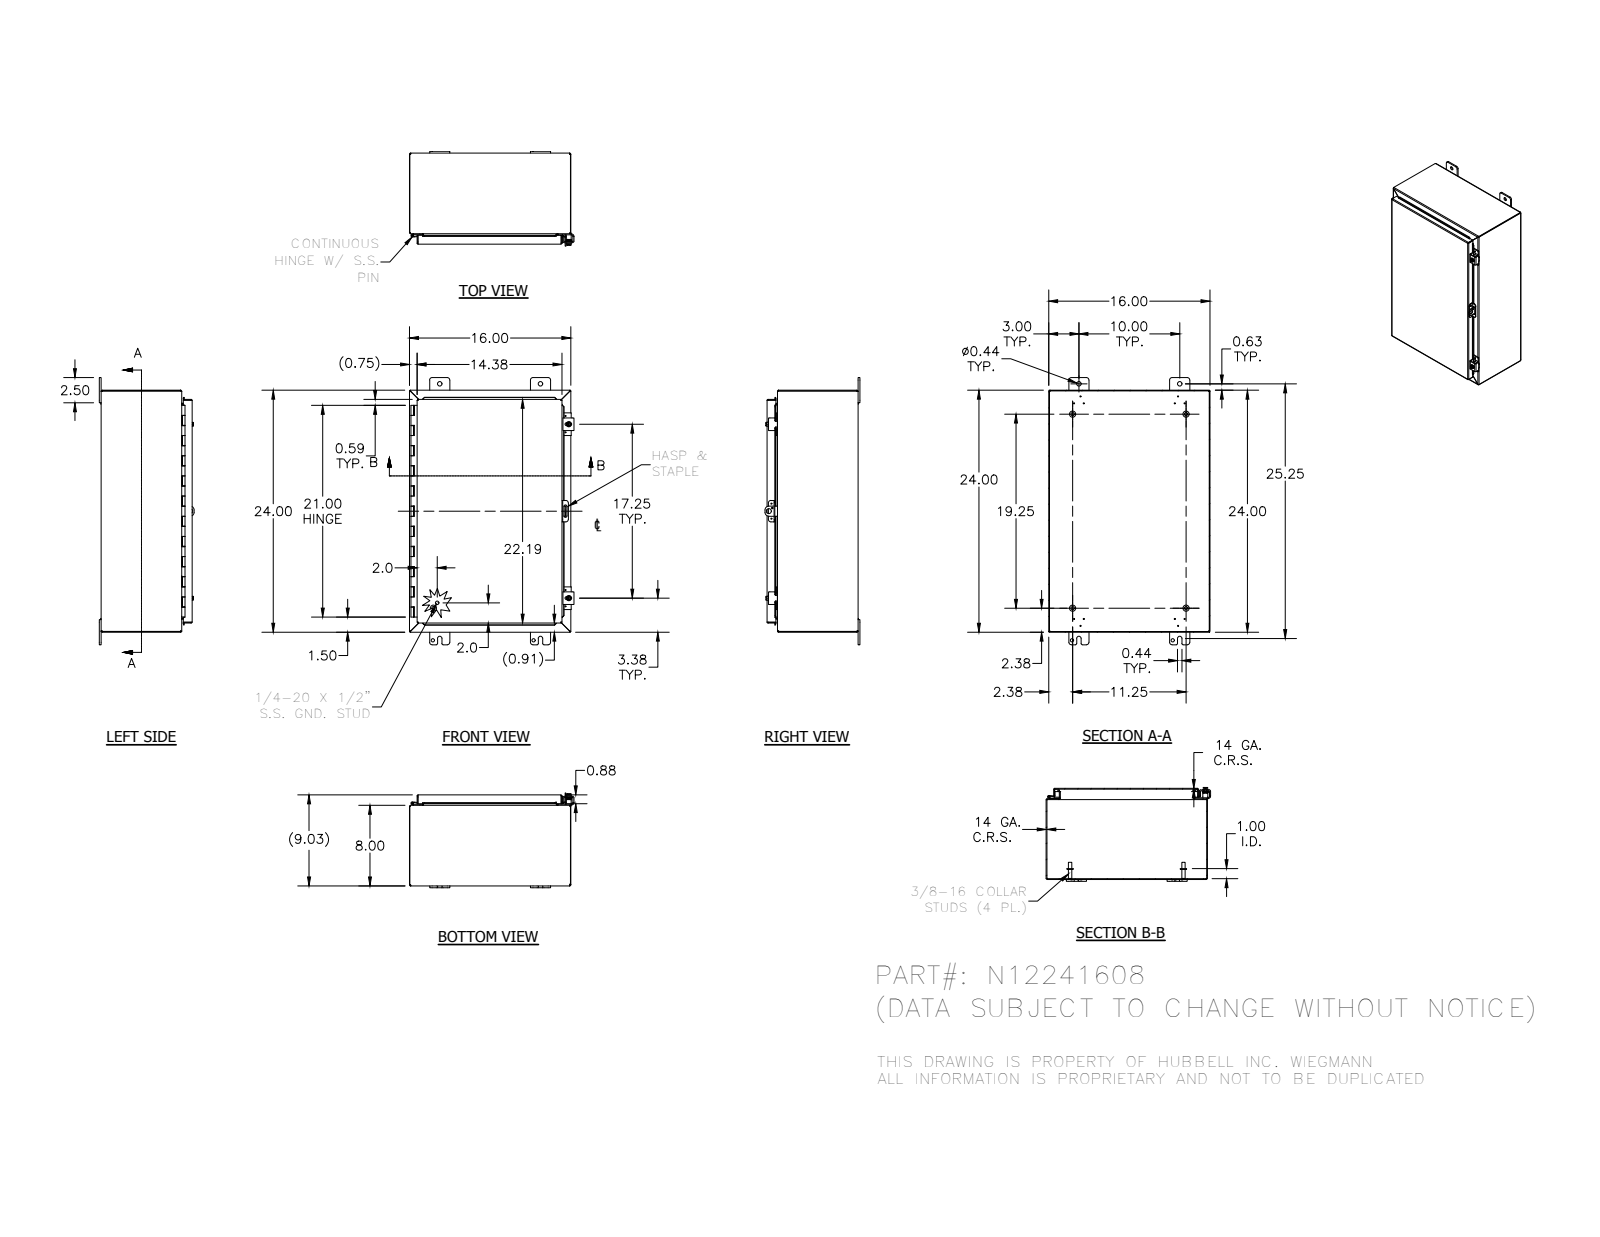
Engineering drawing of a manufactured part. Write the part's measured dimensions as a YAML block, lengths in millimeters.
part_name: "N12241608; 34840; 38420; N12241608BKP (+8 more)"
step_written_by: "Autodesk Inventor 2012 (AUTOMOTIVE_DESIGN)"
units: millimeters
bodies: {solids: 27, faces: 982, planar: 533, cylindrical: 332, other: 117}
overall_size: [673.1, 414.3, 239]
volume: 2150000
surface_area: 2205000
round_holes:
  - {diameter: 3, count: 12}
  - {diameter: 2.8, count: 7}
  - {diameter: 8, count: 4}
  - {diameter: 11.1, count: 4}
  - {diameter: 5.4, count: 2}
  - {diameter: 7.1, count: 2}
  - {diameter: 7.6, count: 2}
  - {diameter: 3.2, count: 1}
  - {diameter: 4, count: 1}
  - {diameter: 12.7, count: 1}
round_bosses_or_shafts:
  - {diameter: 15.9, count: 4}
  - {diameter: 8.4, count: 4}
  - {diameter: 6.4, count: 4}
  - {diameter: 13.2, count: 2}
  - {diameter: 12.7, count: 2}
  - {diameter: 8.9, count: 2}
  - {diameter: 2.9, count: 2}
  - {diameter: 8.6, count: 1}
partial_cylinders:
  - {radius: 0.8, count: 27}
  - {radius: 1.6, count: 25}
  - {radius: 3.2, count: 25}
  - {radius: 6.4, count: 25}
  - {radius: 0.8, count: 23}
  - {radius: 2.7, count: 23}
  - {radius: 1.8, count: 8}
  - {radius: 2.5, count: 4}
face_to_face_distances: [1.9, 227.6, 404.5, 225.7, 229.4, 607.7, 201.3, 26.2, 402.6, 406.4]
hole_center_spacings: [254, 19.3, 21.3, 23.9, 24.6, 50.6, 238.3, 262.8]
